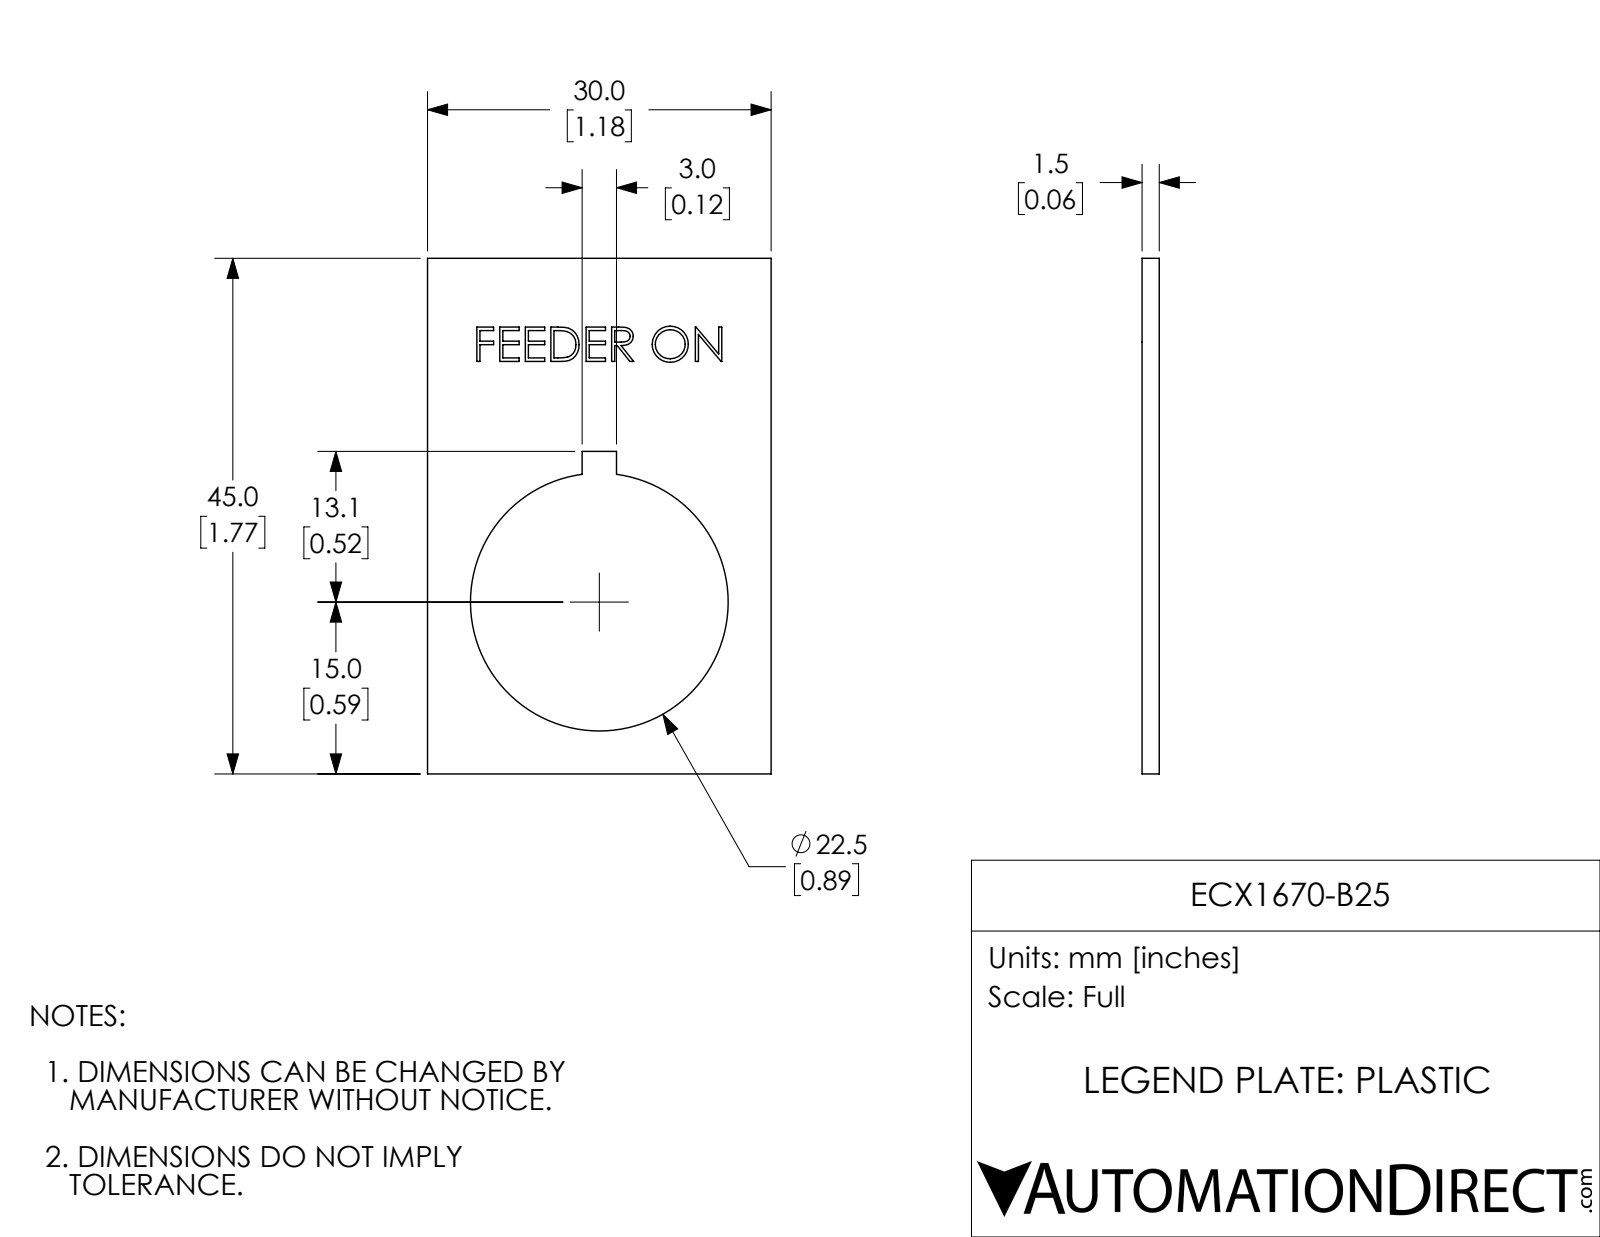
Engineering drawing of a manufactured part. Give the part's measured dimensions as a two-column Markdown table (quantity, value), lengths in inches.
| quantity | value |
| --- | --- |
| part name | ECX1670-B25 |
| STEP written by | SolidWorks 2017 (AUTOMOTIVE_DESIGN) |
| units | inches |
| bodies | 1 solid, 116 faces (93 planar, 3 cylindrical, 20 other) |
| overall size | 1.772 × 1.181 × 0.059 |
| volume | 0.087 in³ |
| surface area | 3.462 in² |
| round holes (diameter × count) | 0.886 × 1 |
| main face-to-face distances | 0.059, 1.181, 1.772, 0.058, 0.531, 0.65, 1.108, 0.663, 0.118, 0.012 |
